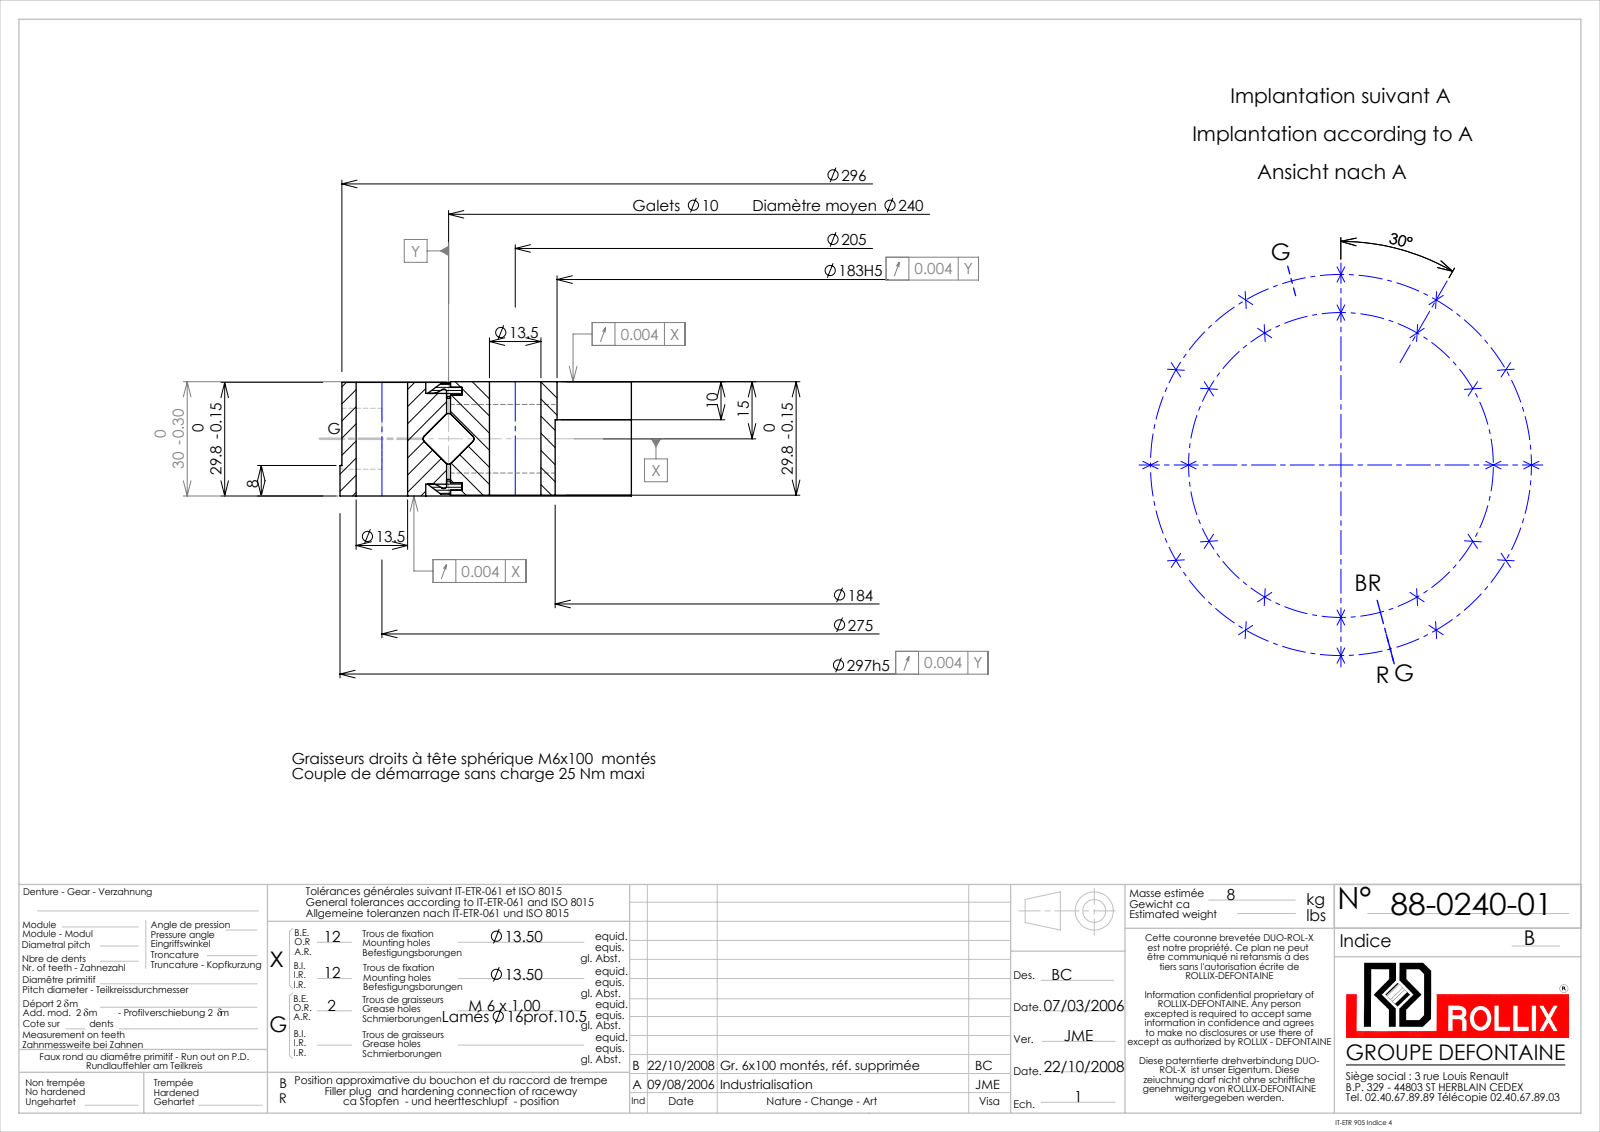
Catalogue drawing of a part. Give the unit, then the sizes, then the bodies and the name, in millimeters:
Units: millimetres
Overall size (bounding box): 297 × 297 × 30
Round holes (diameter × count): ⌀13.5 ×24, ⌀5 ×2, ⌀16 ×2, ⌀183 ×1, ⌀184 ×1, ⌀233 ×1, ⌀239 ×1, ⌀241 ×1, ⌀252 ×1
Round bosses / shafts (diameter × count): ⌀6 ×2, ⌀297 ×1, ⌀296 ×1, ⌀10 ×1
Main face-to-face distances: 29.8, 29.6, 30, 26.5, 3.3, 3.1, 26.7, 3.5, 1.5, 26.3
Hole centre spacings: 70.72, 102.5, 123.77, 137.5, 171.5, 232, 208.58, 35
Volume: 1 061 000 mm³ · Surface area: 253 959 mm²
Bodies: 7 solids, 208 faces (47 planar, 106 cylindrical, 55 other)
Part name (STEP PRODUCT): 88-0240-00
STEP written by: SolidWorks 2016 (CONFIG_CONTROL_DESIGN)
